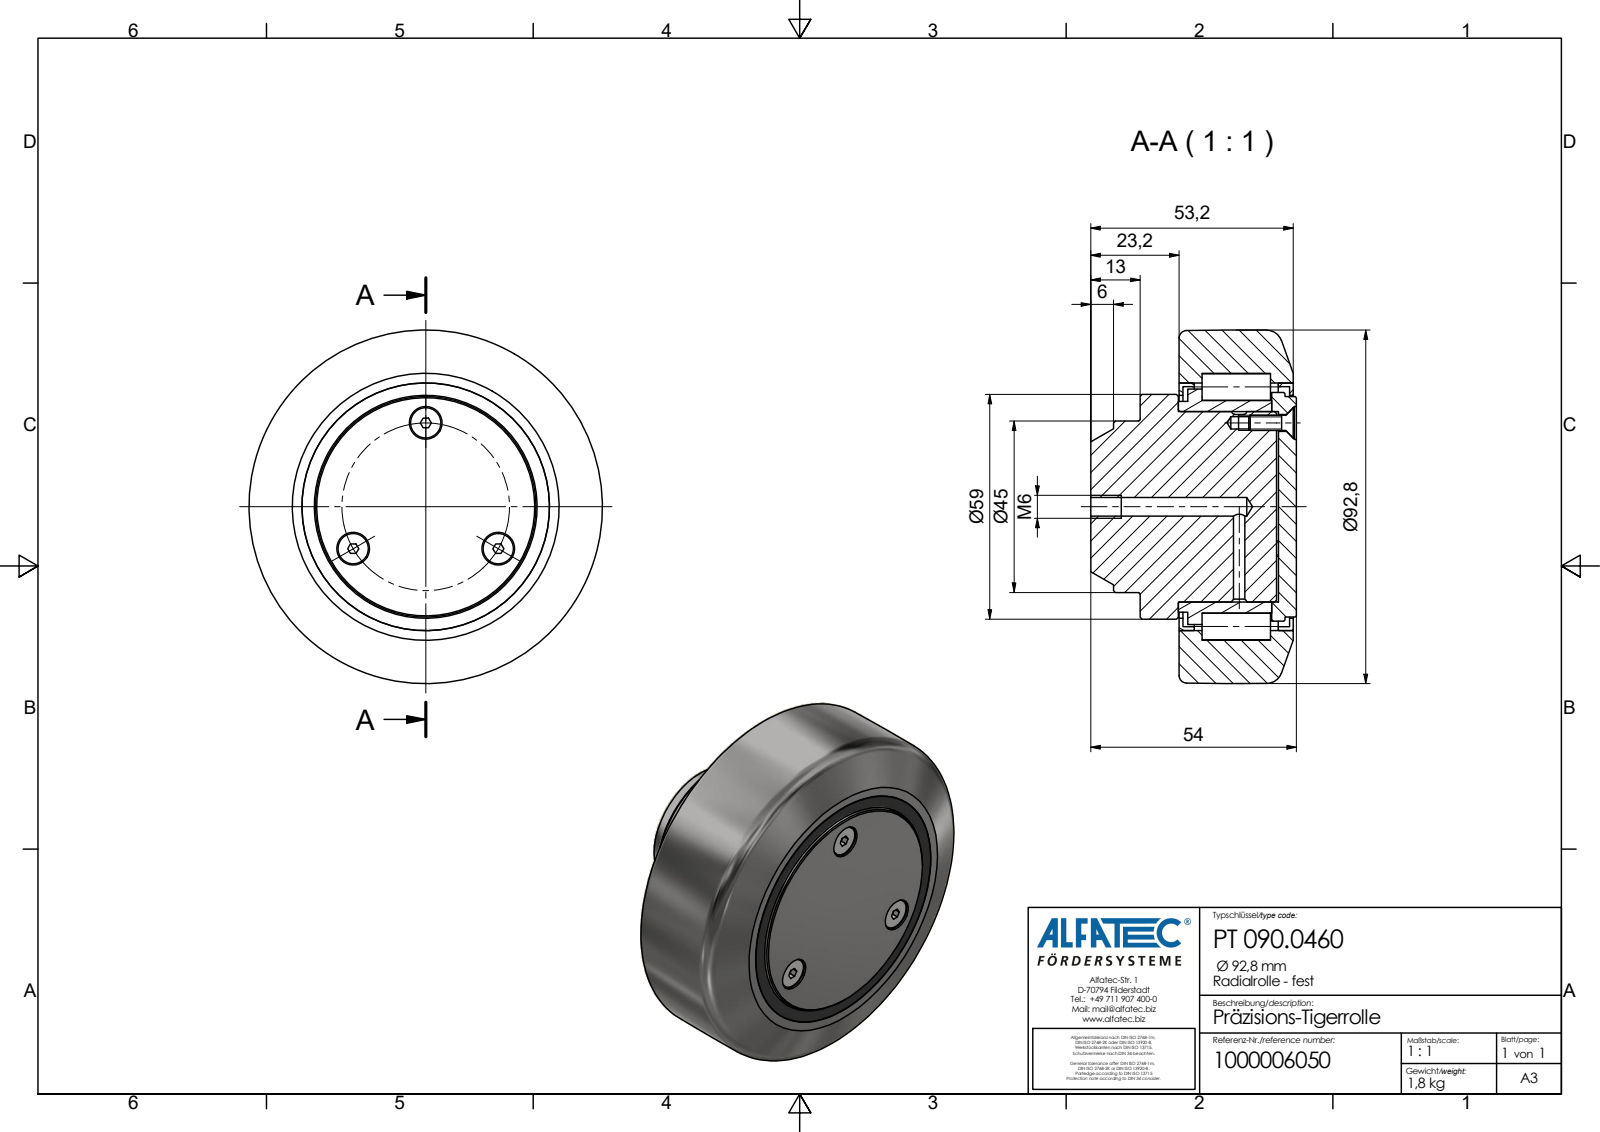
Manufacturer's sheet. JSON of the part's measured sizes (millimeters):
{"part_name": "PT090.0460_Kontur", "step_written_by": "Autodesk Inventor 2020 (AP242_MANAGED_MODEL_BASED_3D_ENGINEERING_MIM_LF)", "units": "millimeters", "bodies": {"solids": 2, "faces": 86, "planar": 41, "cylindrical": 26, "other": 19}, "overall_size": [92.8, 92.8, 54], "volume_mm3": 212154, "surface_area_mm2": 42550, "round_holes": [[8.6, 3], [3, 2], [4.92, 1], [50, 1], [58.5, 1], [63, 1], [65, 1], [70, 1]], "round_bosses_or_shafts": [[8, 3], [61.8, 1], [60, 1], [59, 1], [57.8, 1], [55.8, 1], [55.3, 1], [48.5, 1]], "face_to_face_distances": [30.8, 6, 24, 30, 0.8, 29.2, 23, 23.2, 24.8, 10.2], "hole_center_spacings": [22, 38.1]}
